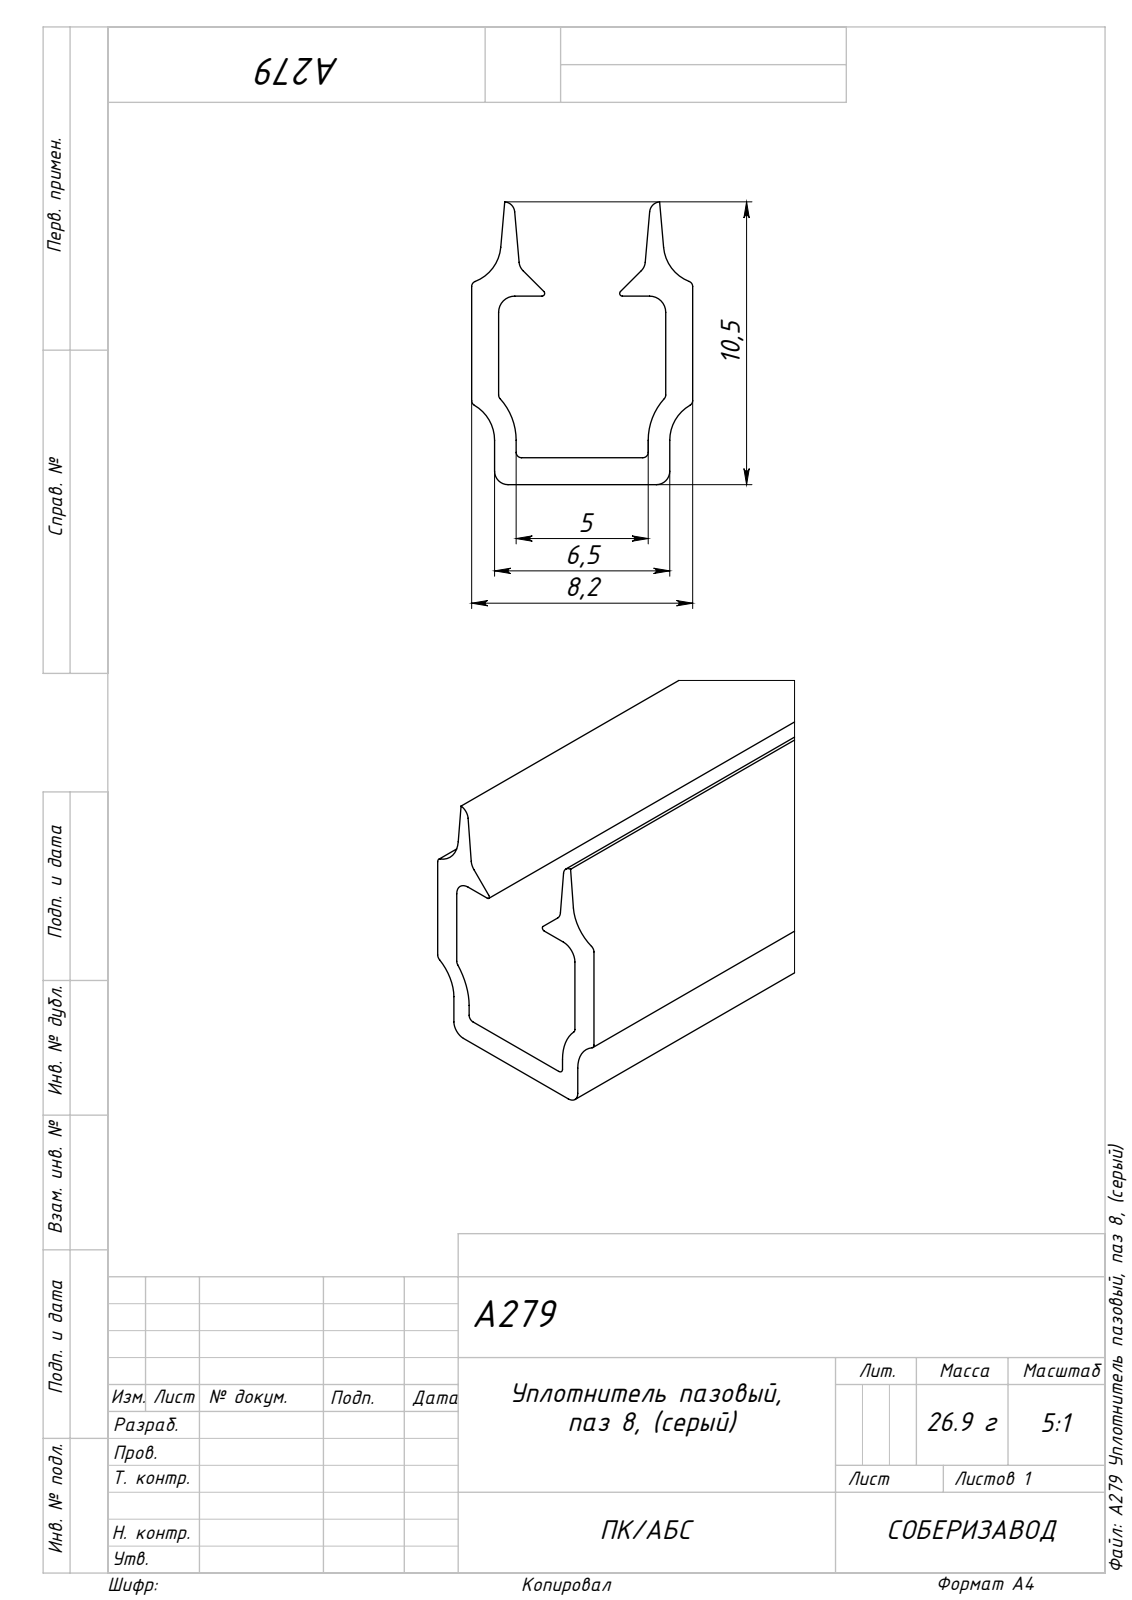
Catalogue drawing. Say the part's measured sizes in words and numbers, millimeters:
The part is named "A279 Уплотнитель пазовый, паз 8, (серый); A279 Уплотнитель пазовый, паз 8, (серый)_А297, Уплотнитель пазовый, паз 8, (серый), подробная модель". Its 3-D file was written by "SolidWorks 2026 (CONFIG_CONTROL_DESIGN)". It is 1 solid with 45 faces: 20 planar, 25 cylindrical and 0 other. Overall it measures 1000 by 10.5 by 8.2 millimeters. Its volume is 25 161 cubic millimeters and its surface area 56 678 square millimeters. Partial cylindrical surfaces (rounded edges, fillets, slot ends): 8 of radius 0.2, 4 of radius 0.5, 4 of radius 1.5, 2 of radius 0.1, 2 of radius 0.41, 2 of radius 0.6, 2 of radius 2.3. The main face-to-face distances are 1, 7.2, 8.2, 5.39, 6.2, 0.85, 7.35, 6.35, 7, 6.
